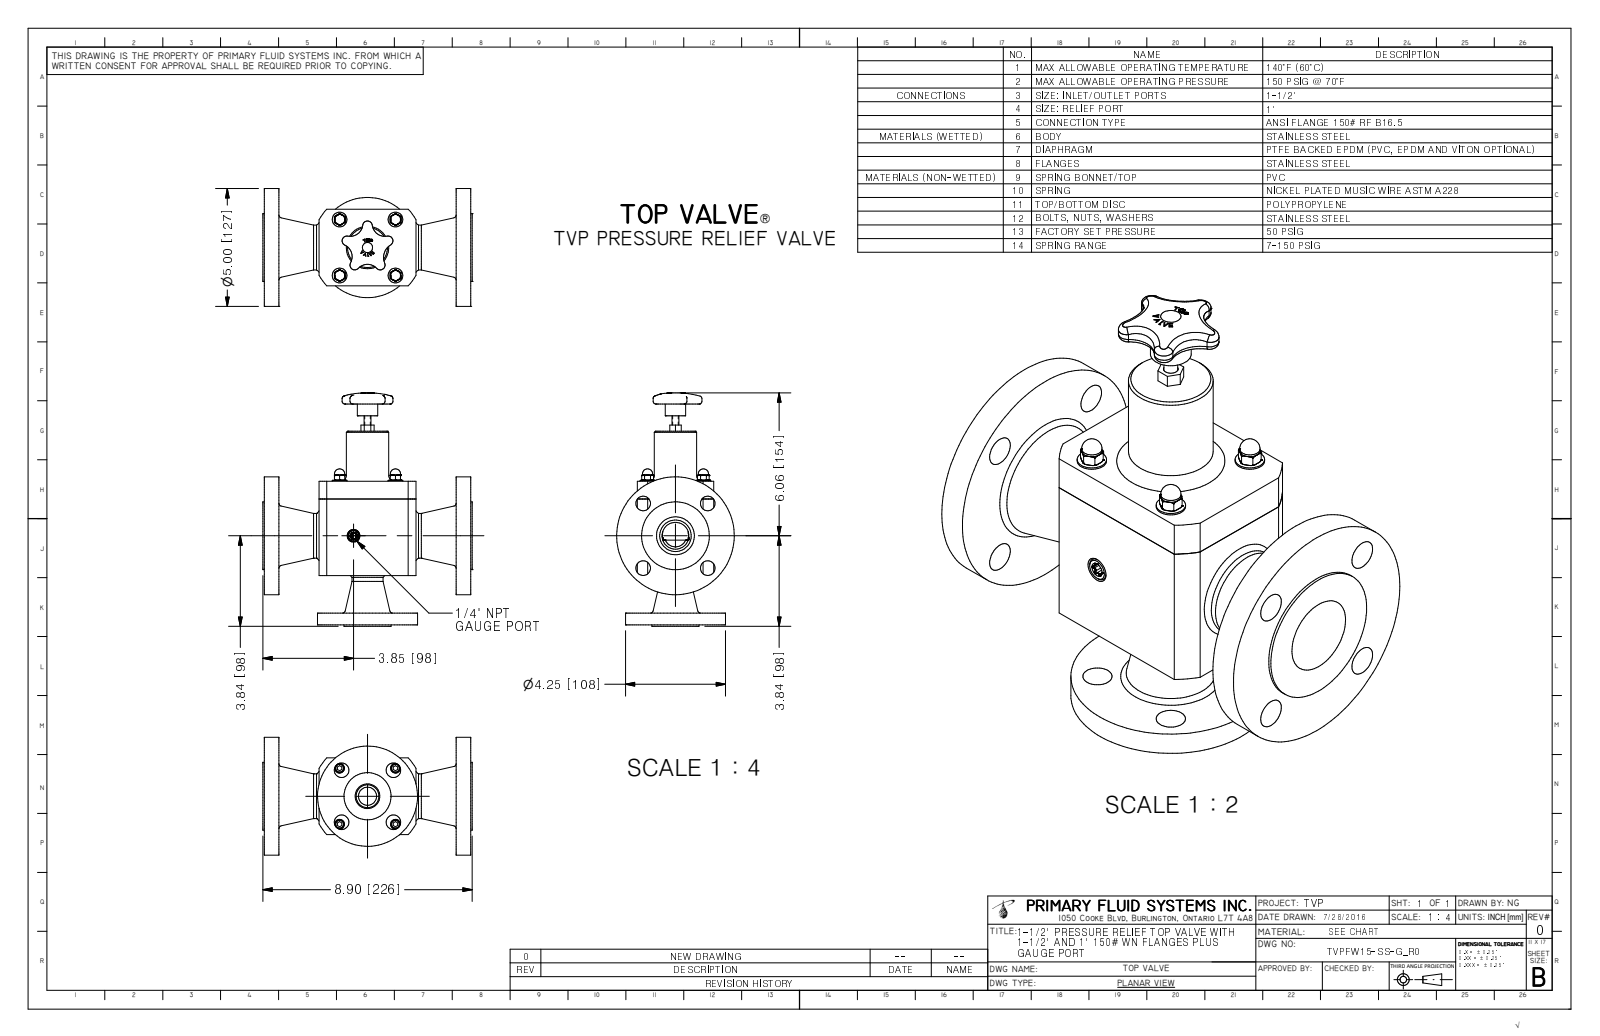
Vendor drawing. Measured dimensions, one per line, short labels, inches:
name: TVPFW15-SS-G_R0
written by: Autodesk Inventor 2009 (AUTOMOTIVE_DESIGN)
unit: in
bodies: 1 solid, 398 faces (162 planar, 73 cylindrical, 163 other)
size: 9.9 × 8.895 × 5
volume: 91.58 in³; area: 298.8 in²
holes: 8× ⌀0.62, 4× ⌀0.175, 1× ⌀1.049, 1× ⌀1.61
bosses: 4× ⌀0.625, 4× ⌀0.433, 4× ⌀0.375, 1× ⌀5, 1× ⌀4.25, 1× ⌀2.88, 1× ⌀2, 1× ⌀1.9
rounds: 6× R0.027, 5× R0.085, 5× R0.205, 4× R0.536, 4× R0.656, 1× R0.625, 1× R0.745, 1× R2.375
face distances: 0.62, 8.15, 3.25, 7.53, 8.77, 2.322, 6.448, 1.702, 5.828, 2.09
hole spacings: 1.56, 1.94, 2.206, 2.292, 2.743, 0.119, 0.12, 1.679
